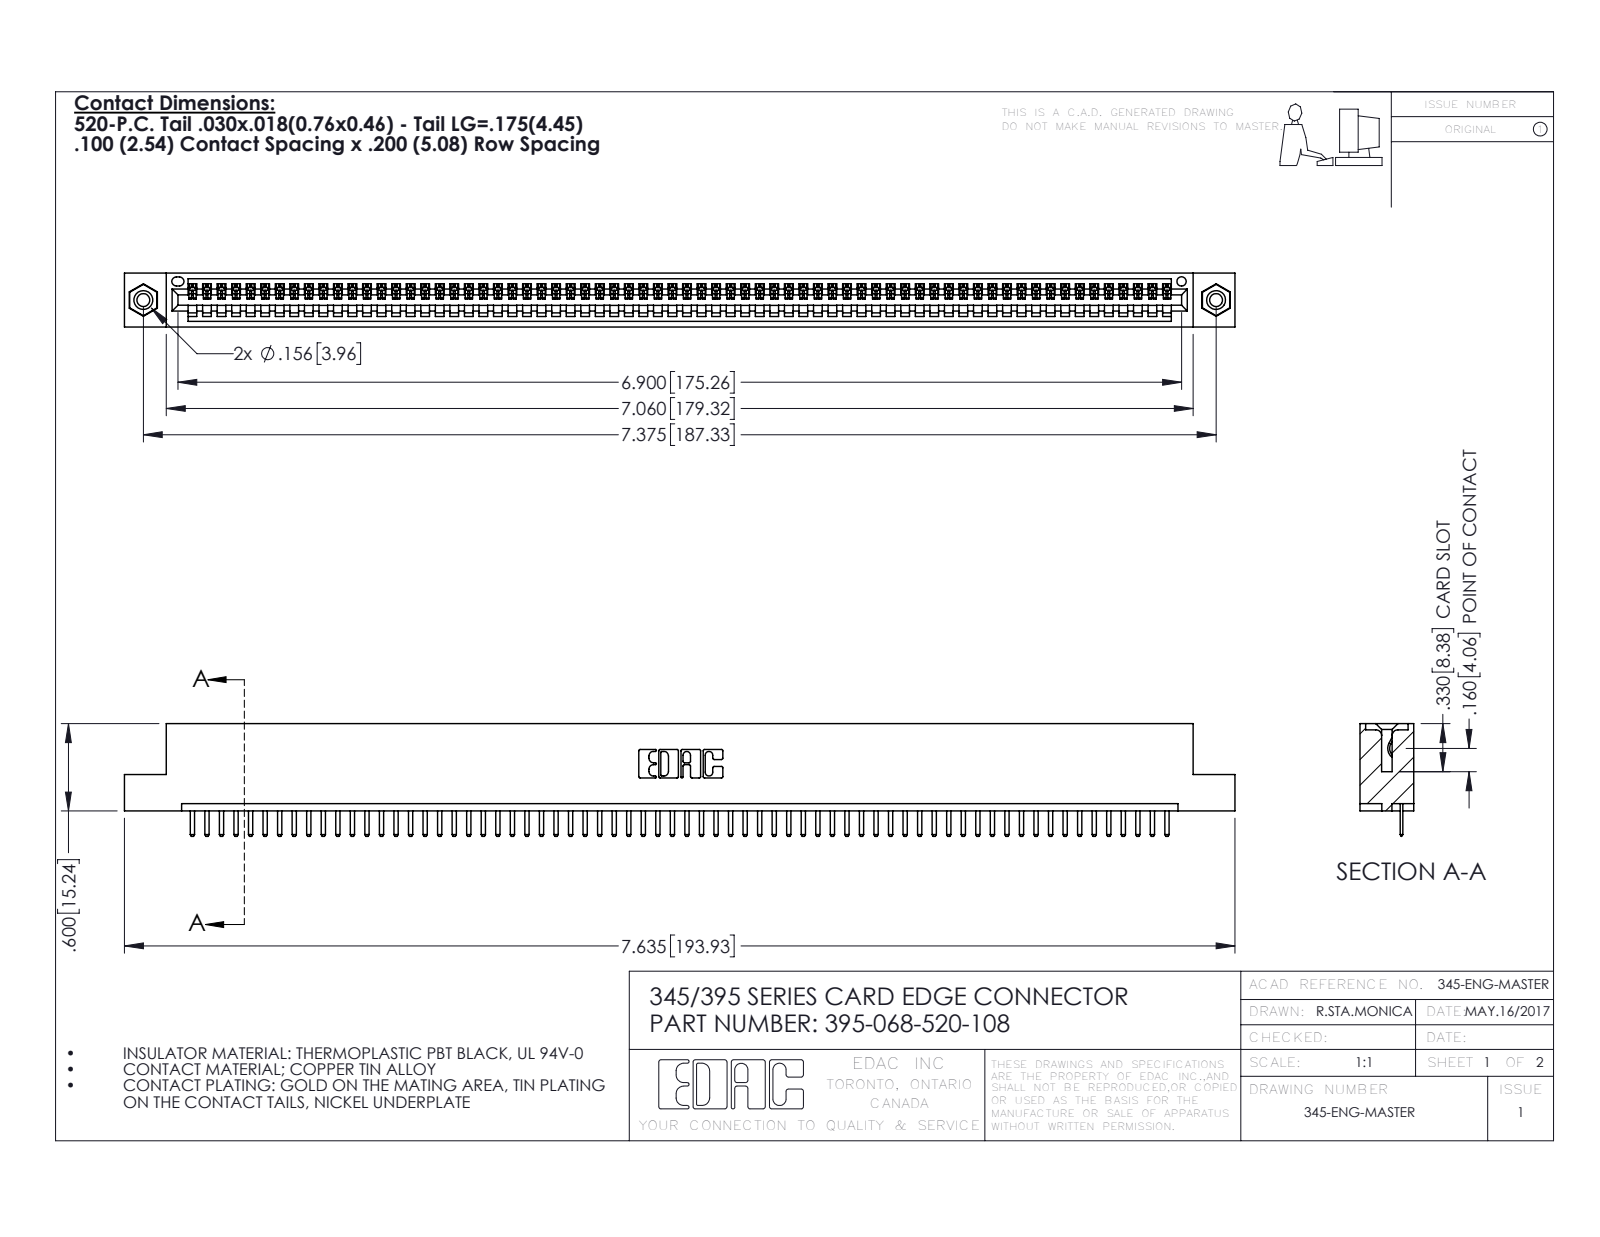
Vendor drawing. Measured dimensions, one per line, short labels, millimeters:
name: 345-292-001_345-293-120; 395-068-520-108; 345-250-001_345-250-003-102; 345 Part_Flush Mounting Lugs - 0.156 Dia-TI
written by: SolidWorks 2016 (CONFIG_CONTROL_DESIGN)
unit: mm
bodies: 71 solids, 4402 faces (2968 planar, 1418 cylindrical, 16 other)
size: 193.9 × 19.7 × 9.4
volume: 18 440 mm³; area: 24 230 mm²
holes: 2× ⌀2.3, 2× ⌀3.2, 2× ⌀4, 1× ⌀1.6
bosses: 2× ⌀3.9
rounds: 138× R0.3, 136× R0.2, 22× R0.3, 6× R0.2, 6× R0.8, 3× R0.7, 2× R0.8, 2× R1
face distances: 1.8, 7.6, 9.4, 5.1, 2.5, 6.9, 0.6, 5.7, 1.8, 3.8
hole spacings: 6.9, 181.3, 187.3
